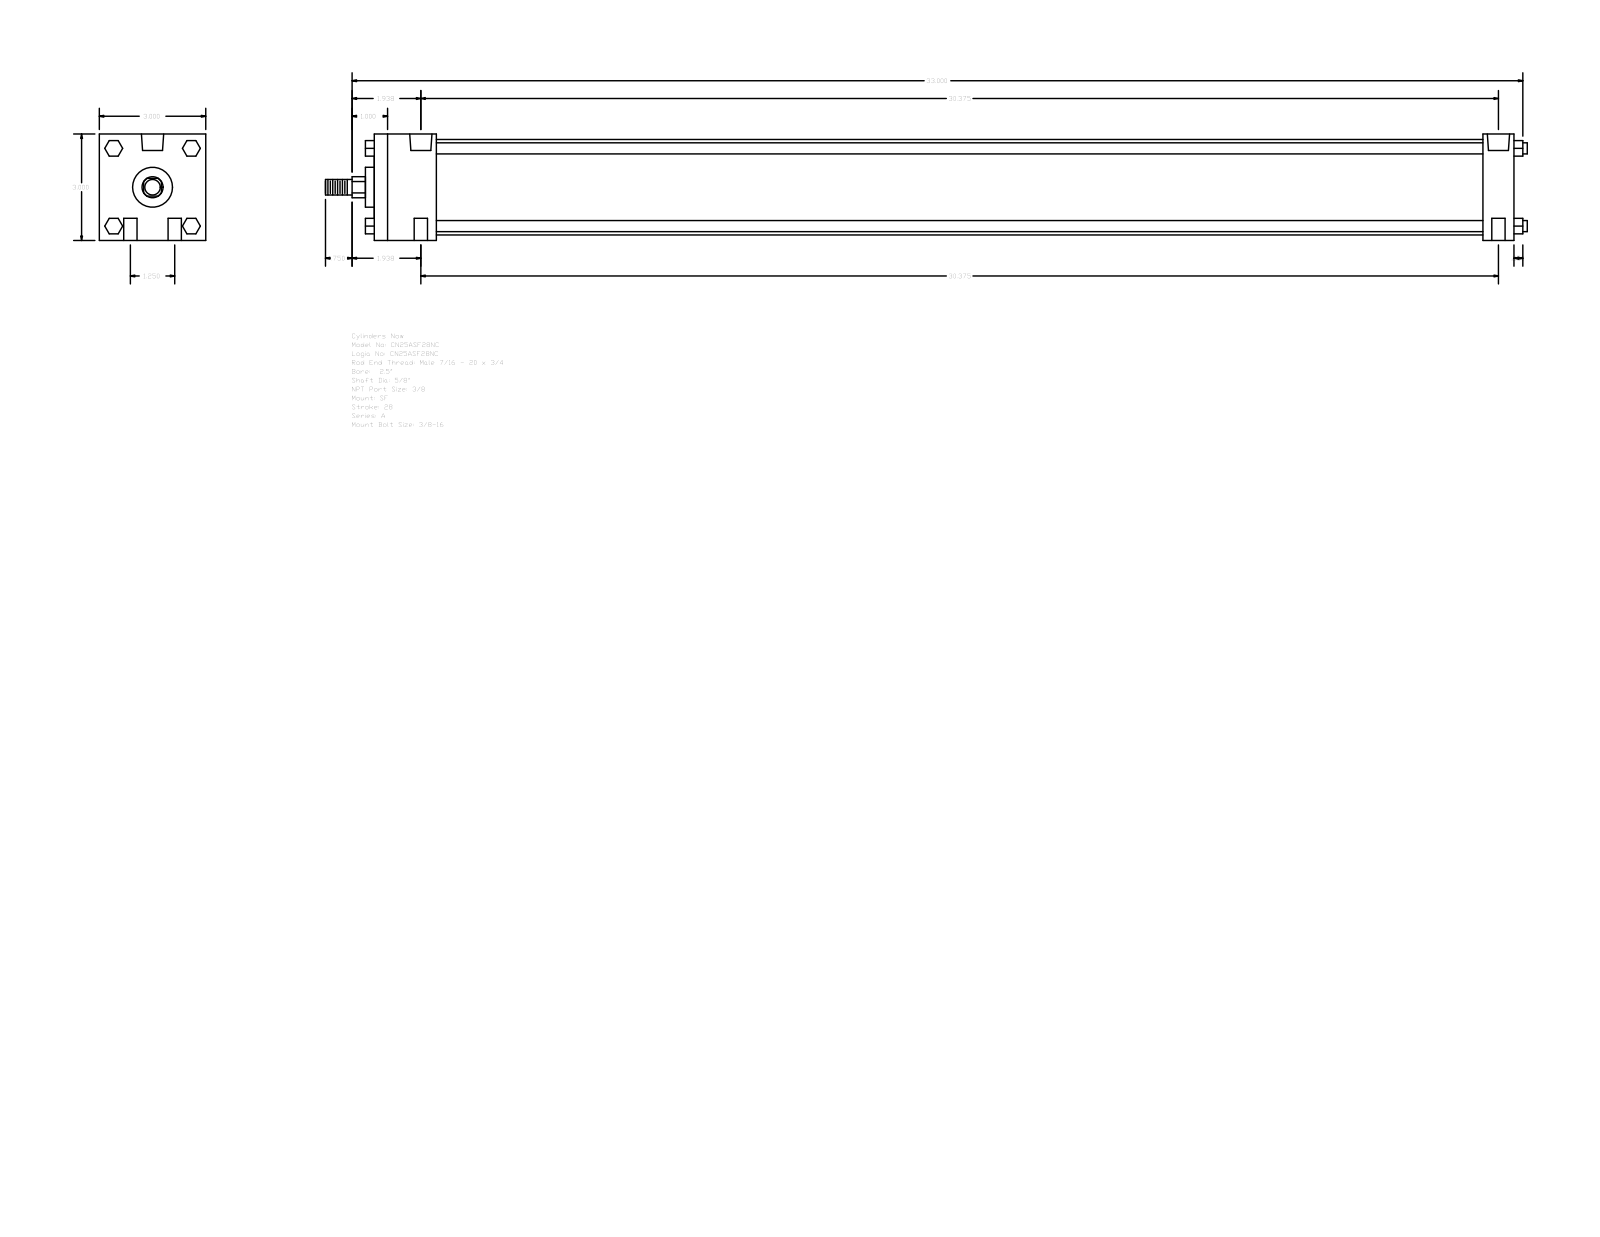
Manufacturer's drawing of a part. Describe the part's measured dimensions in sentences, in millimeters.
The part is named "A_SF__0250_0.625". Its 3-D file was written by "GSSL Pune (CONFIG_CONTROL_DESIGN)". It is 0 solids with 124 faces: 94 planar, 30 cylindrical and 0 other. Overall it measures 860.42 by 76.2 by 76.2 millimeters. Round holes: 4 of diameter 9.53, 2 of diameter 5.56, 2 of diameter 15.93. Round bosses or shafts: 4 of diameter 7.94, 1 of diameter 68.33, 1 of diameter 28.57, 1 of diameter 15.88, 1 of diameter 11.11. Partial cylindrical surfaces (rounded edges, fillets, slot ends): 1 of radius 7.54. The main face-to-face distances are 76.2, 815.97, 44.45, 793.74, 22.23, 749.29, 771.52, 6.35, 822.32, 50.8. The hole center spacings are 15.88, 771.69, 771.53, 31.76, 772.18, 776.29.
